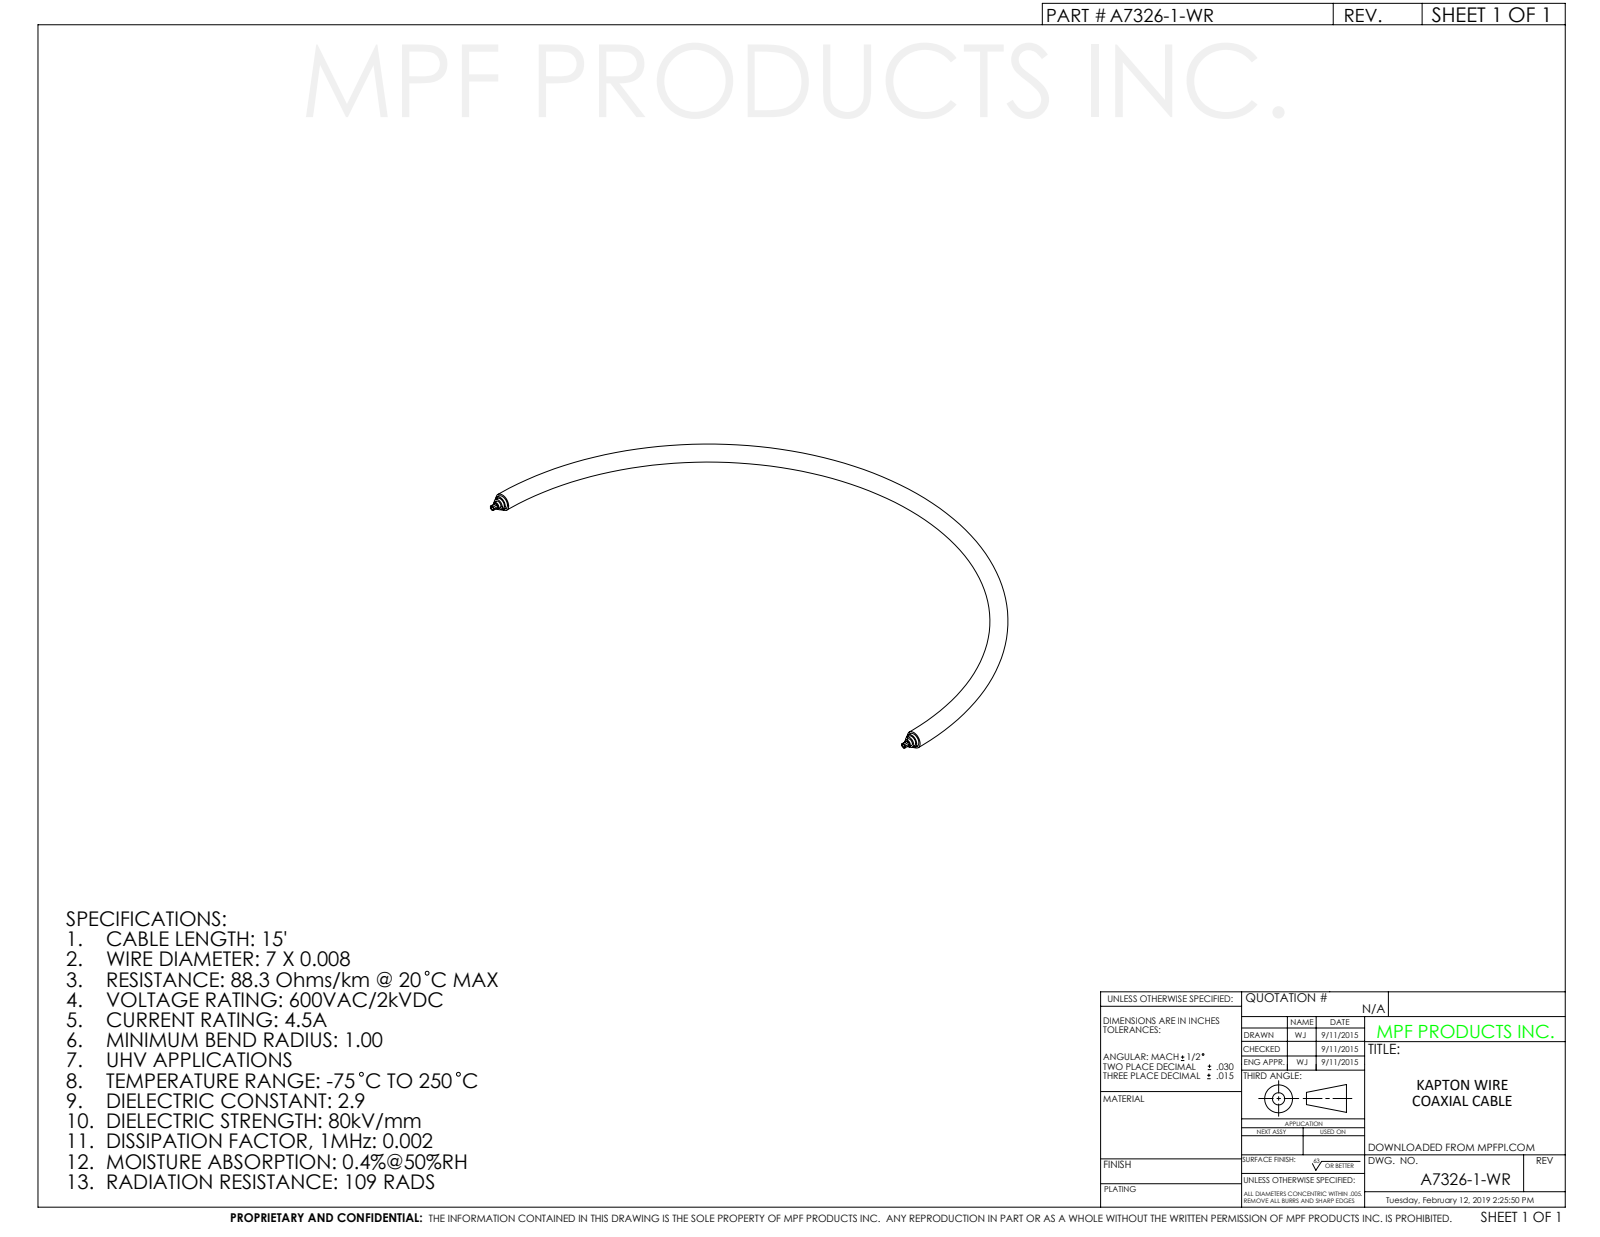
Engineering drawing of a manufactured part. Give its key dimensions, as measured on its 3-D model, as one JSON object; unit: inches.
{"part_name": "A7326-1-WR", "step_written_by": "SolidWorks 2012 (CONFIG_CONTROL_DESIGN)", "units": "inches", "bodies": {"solids": 10, "faces": 330, "planar": 20, "cylindrical": 86, "other": 224}, "overall_size": [0.35, 0.05, 0.05], "round_holes": [[0.025, 1], [0.033, 1], [0.047, 1]], "round_bosses_or_shafts": [[0.008, 7], [0.05, 1], [0.046, 1], [0.044, 1], [0.032, 1]], "face_to_face_distances": [0.225, 0.35, 0.125, 0.3, 0.075, 0.05, 0.2, 0.025, 0.1, 0.15]}
